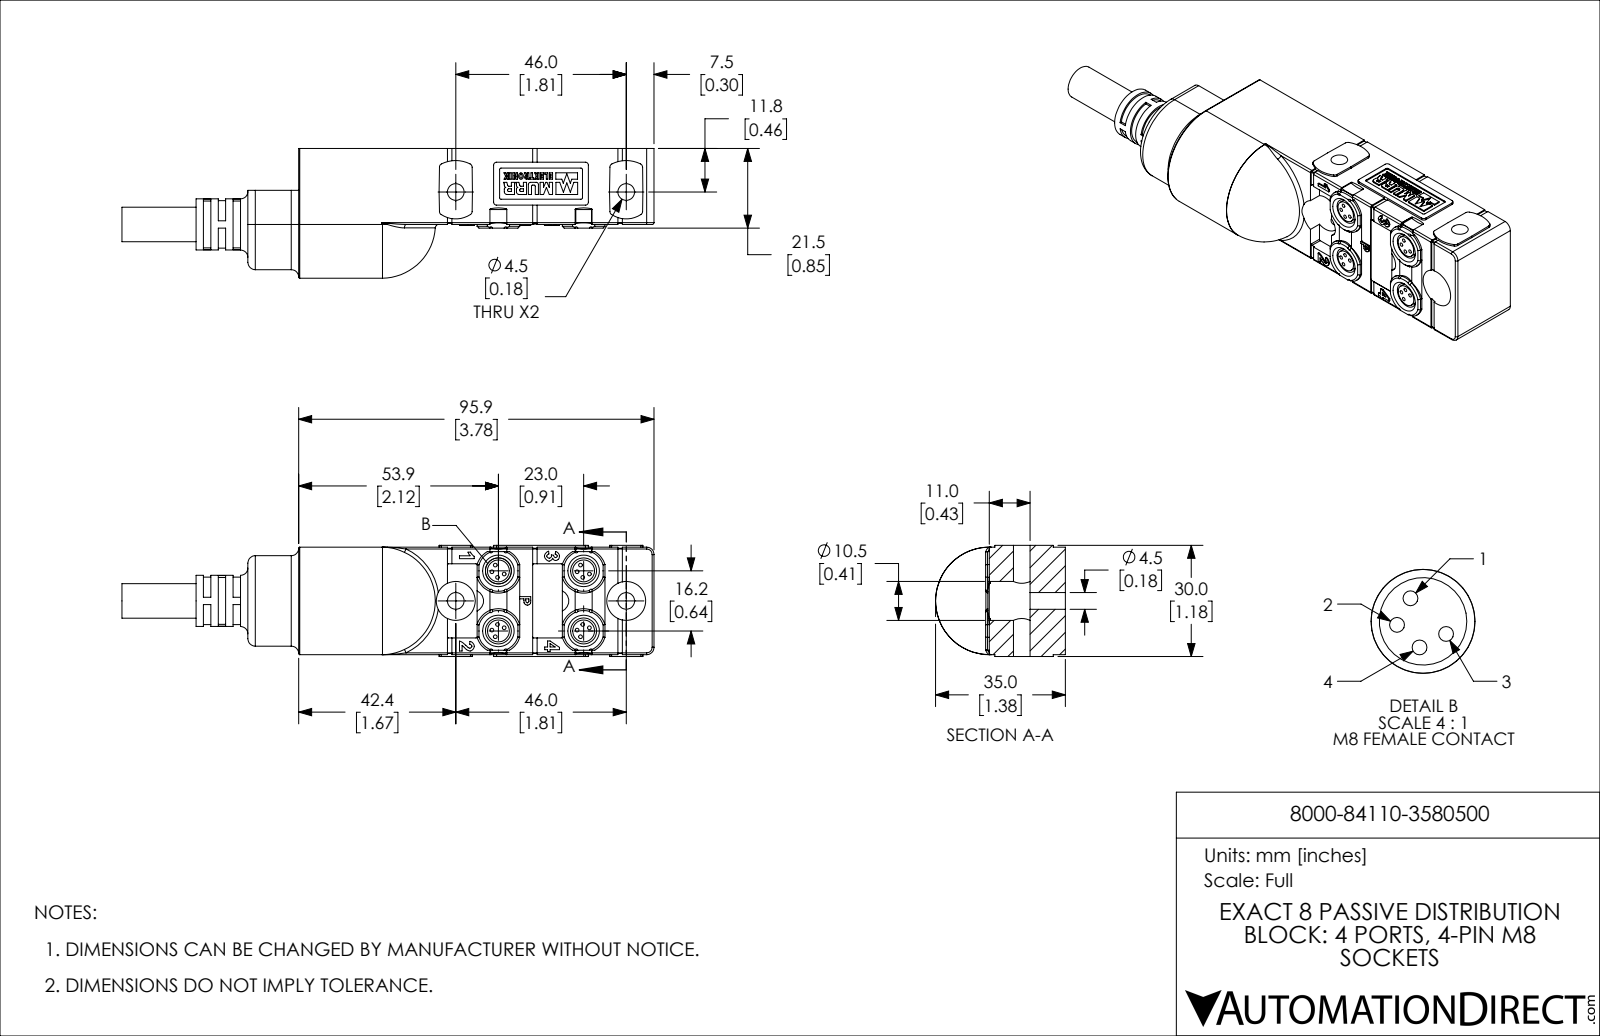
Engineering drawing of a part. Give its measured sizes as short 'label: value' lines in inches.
name: 8000-84110-3580500
written by: SolidWorks 2019 (CONFIG_CONTROL_DESIGN)
unit: in
bodies: 1 solid, 983 faces (585 planar, 293 cylindrical, 105 other)
size: 5.654 × 1.378 × 1.181
volume: 4.519 in³; area: 25.71 in²
holes: 16× ⌀0.039, 4× ⌀0.177, 4× ⌀0.276, 2× ⌀0.413
bosses: 4× ⌀0.232, 1× ⌀0.543, 1× ⌀0.504, 1× ⌀0.449, 1× ⌀0.366
rounds: 19× R0.02, 12× R0.008, 10× R0.012, 8× R0.039, 6× R0.079, 6× R0.394, 4× R0.012, 4× R0.012
face distances: 1.142, 0.02, 1.161, 0.807, 0.795, 0.433, 0.362, 0.445, 1.181, 3.776
hole spacings: 0.07, 0.906, 0.08, 0.133, 0.085, 0.134, 0.54, 0.554
